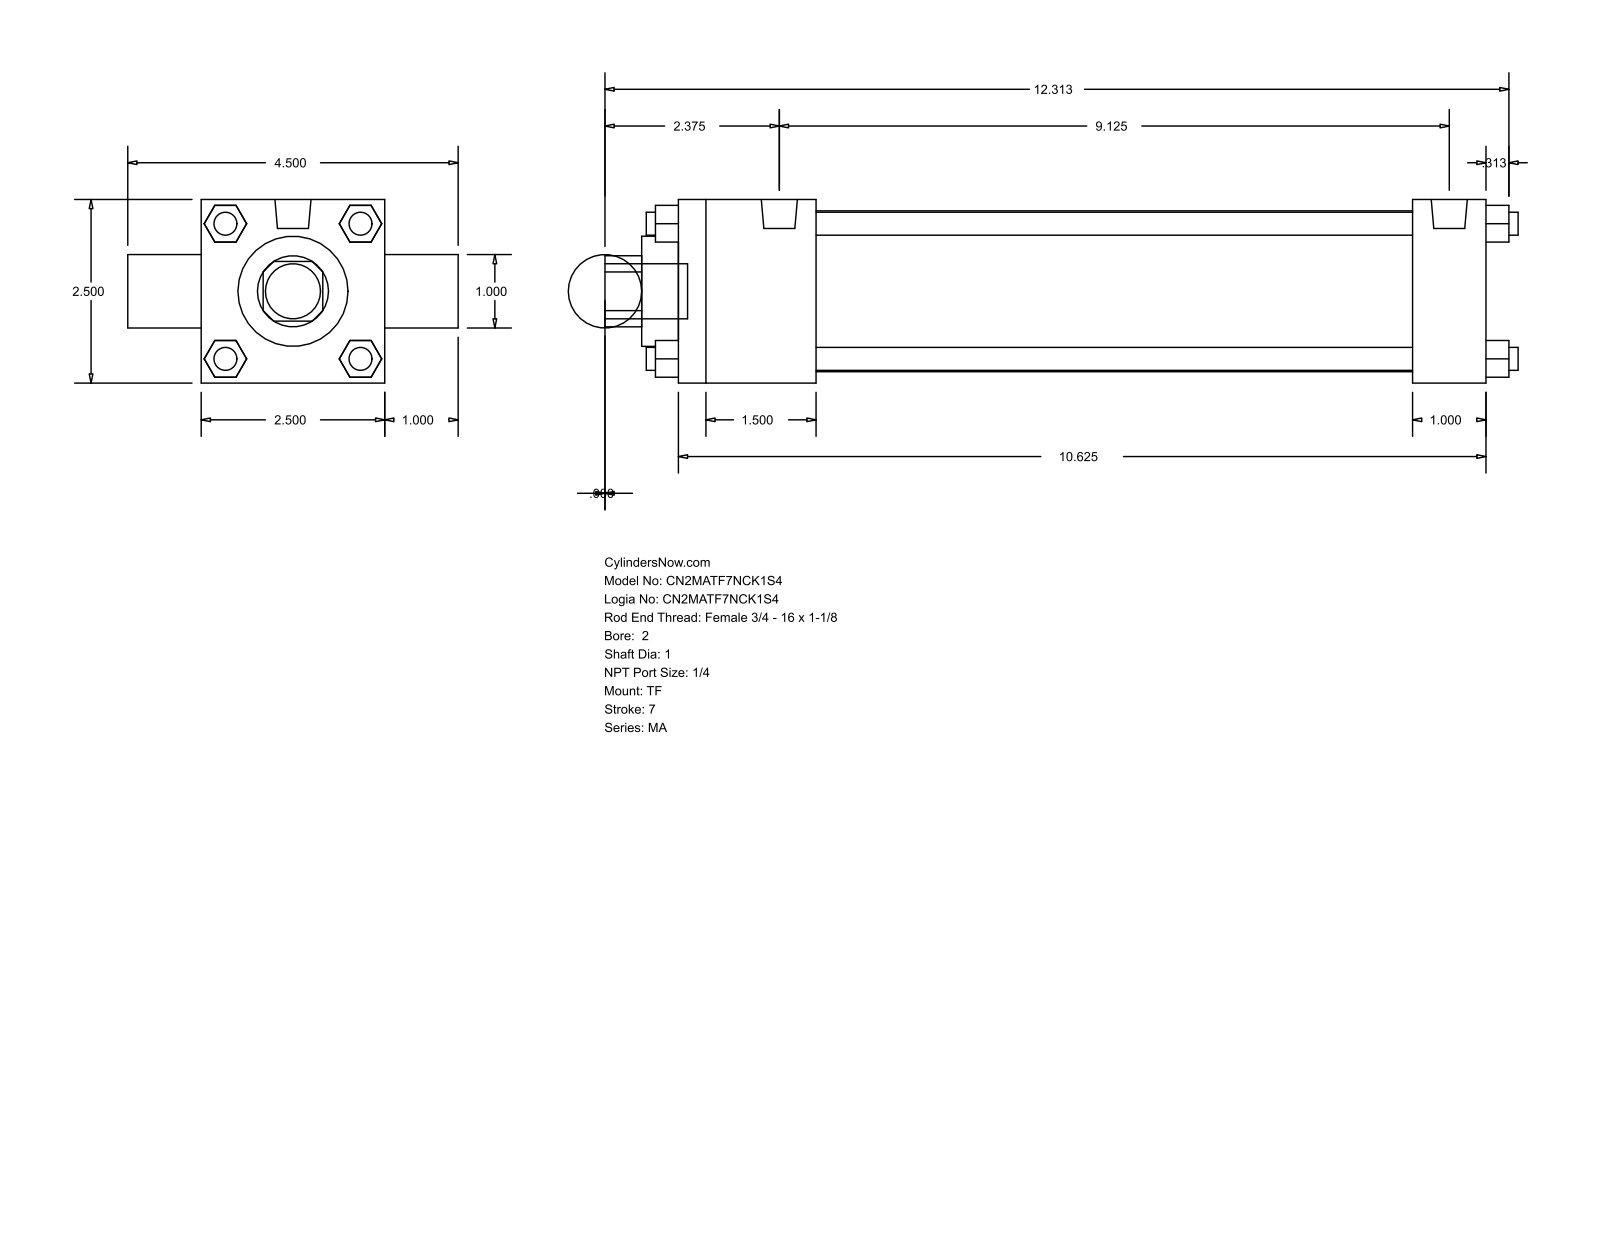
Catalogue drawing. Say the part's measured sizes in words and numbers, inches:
The part is named "MA_TF__0200_1". Its 3-D file was written by "GSSL Pune (CONFIG_CONTROL_DESIGN)". It is 0 solids with 120 faces: 92 planar, 28 cylindrical and 0 other. Overall it measures 12.437 by 4.5 by 2.5 inches. Round holes: 2 of diameter 1, 1 of diameter 1.5, 1 of diameter 2.19. Round bosses or shafts: 7 of diameter 0.313, 2 of diameter 0.492, 1 of diameter 0.75. Partial cylindrical surfaces (rounded edges, fillets, slot ends): 1 of radius 0.484. The main face-to-face distances are 2.5, 1, 11, 0.5, 1.875, 10, 8.125, 9.125, 3.5, 0.92.
